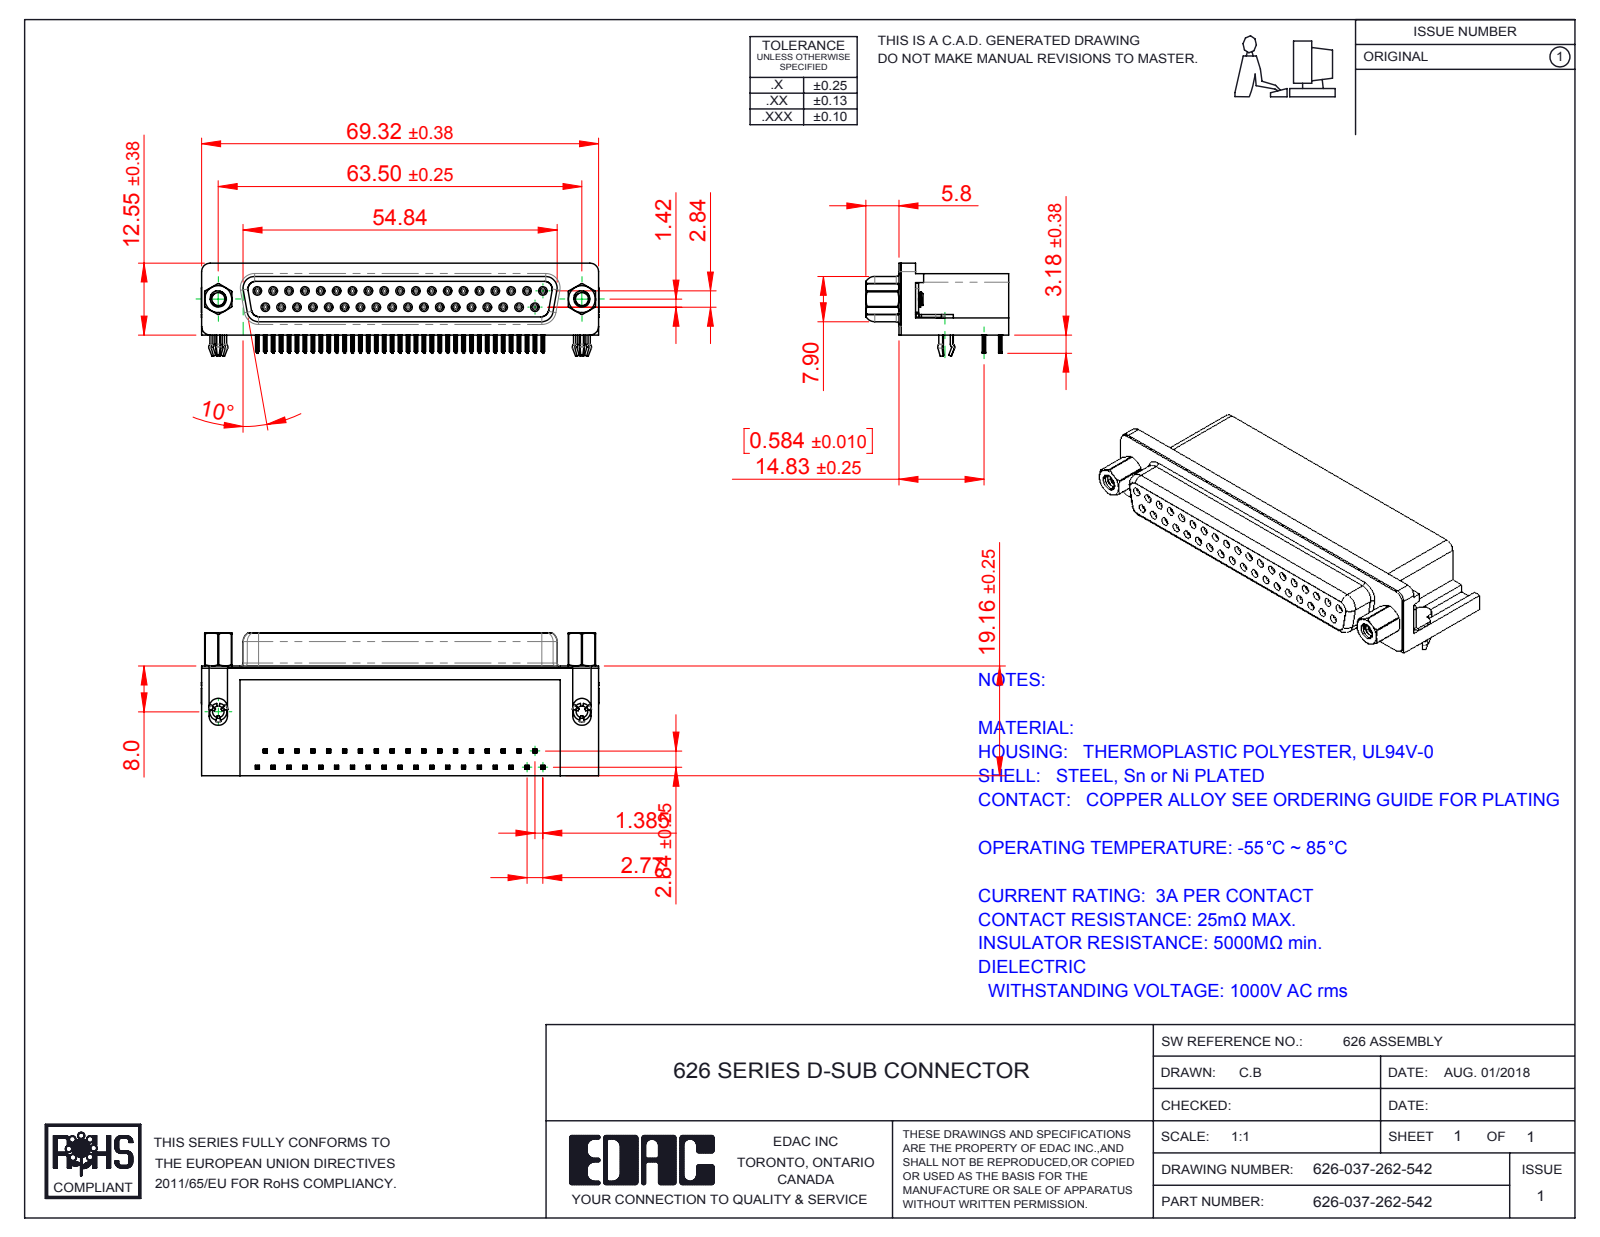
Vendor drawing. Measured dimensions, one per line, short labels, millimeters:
name: 626-037-262-542; 626 Housing_37 Socket; 626 3 Prong Board Lock; 626 Contact Bottom (+3 more)
written by: SolidWorks 2016 (CONFIG_CONTROL_DESIGN)
unit: mm
bodies: 43 solids, 5702 faces (2546 planar, 1338 cylindrical, 1818 other)
size: 69.4 × 24.96 × 16.25
volume: 14 850 mm³; area: 15 560 mm²
holes: 37× ⌀0.8, 37× ⌀0.9, 2× ⌀2, 2× ⌀2.29, 2× ⌀4, 2× ⌀4.8, 2× ⌀5
bosses: 37× ⌀1.2, 2× ⌀4.9, 2× ⌀3, 2× ⌀2.79
rounds: 296× R0.1, 148× R0.15, 74× R0.35, 37× R0.34, 18× R0.28, 18× R1, 8× R1.35, 8× R1.6
face distances: 10.34, 0.4, 2.84, 6.2, 18.76, 0.45, 7.1, 3.17, 0.85, 7.05
hole spacings: 3.16, 2.77, 5.54, 8.31, 11.08, 22.16, 13.85, 19.39
